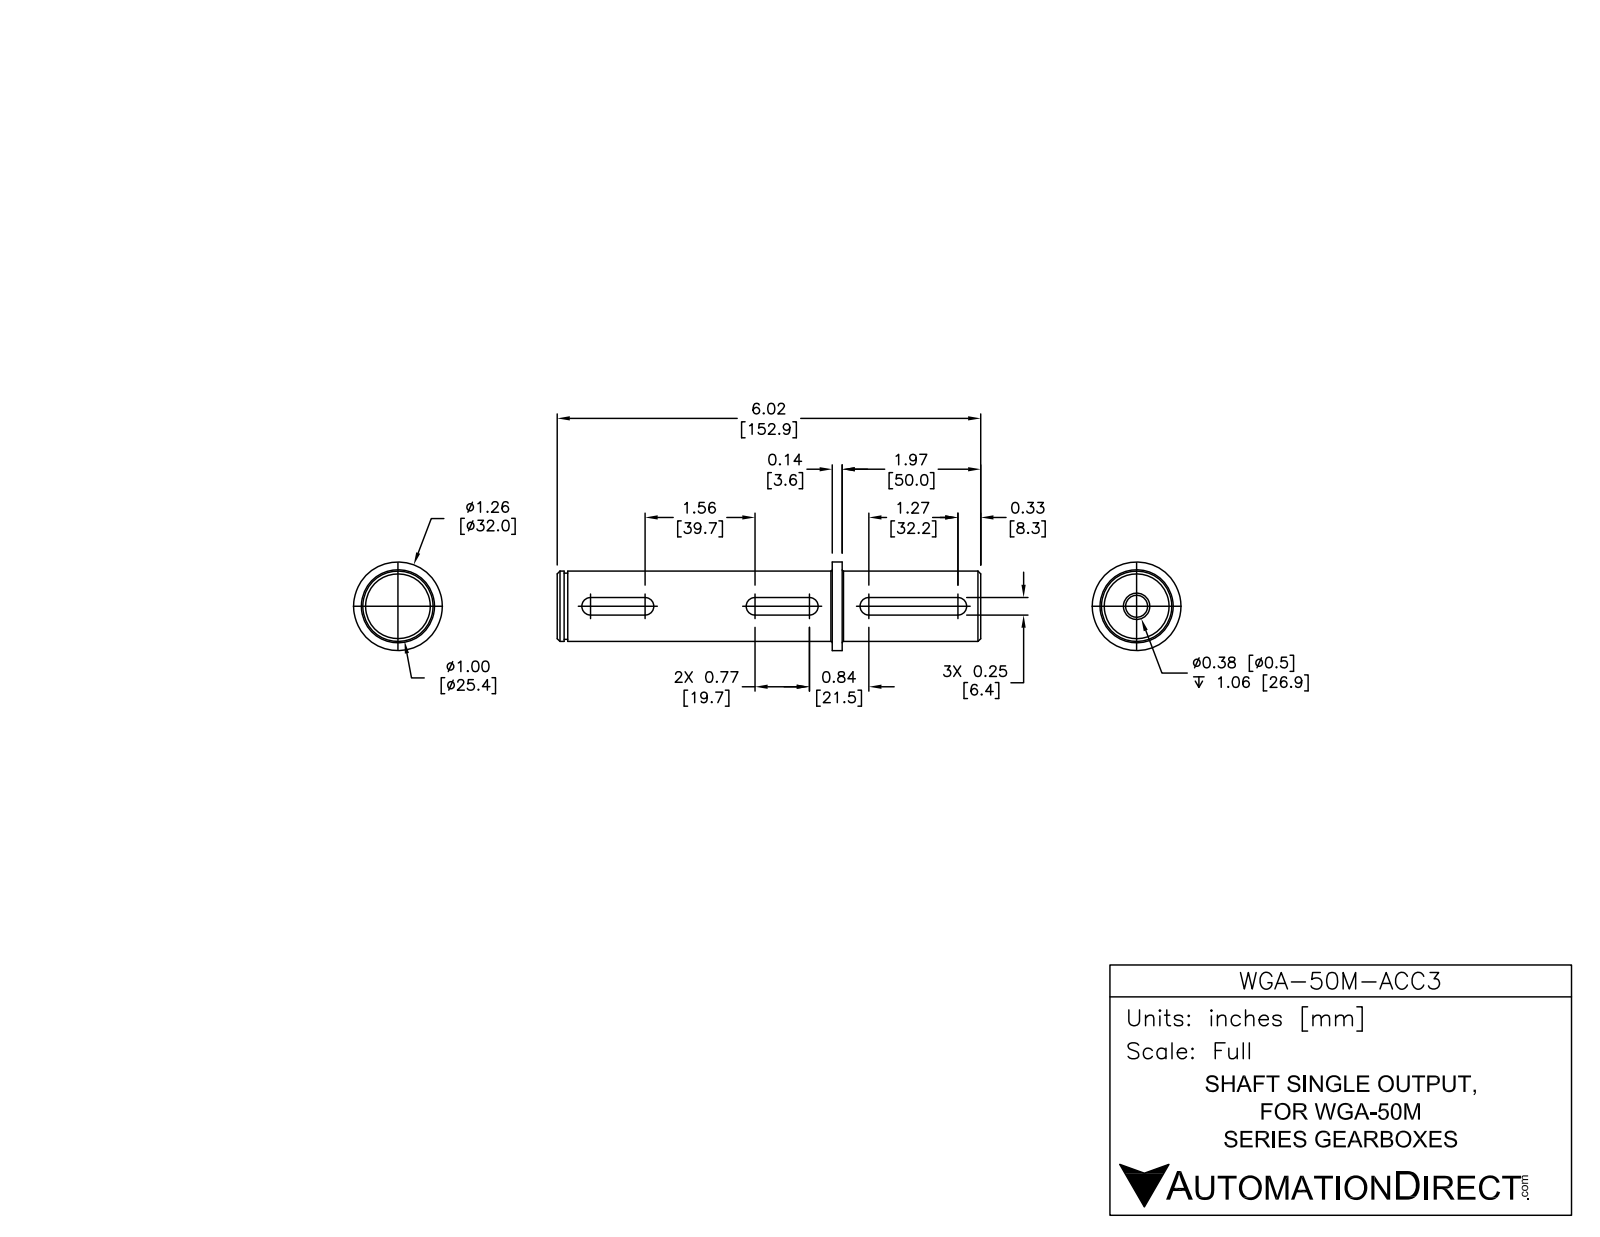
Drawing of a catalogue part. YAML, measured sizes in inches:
part_name: "WGA-50M-ACC3"
step_written_by: "SolidWorks 2014 (AUTOMOTIVE_DESIGN)"
units: inches
bodies: {solids: 1, faces: 46, planar: 16, cylindrical: 20, other: 10}
overall_size: [6.02, 1.26, 1.26]
volume: 4.559
surface_area: 23.7
round_holes:
  - {diameter: 0.313, count: 1}
  - {diameter: 0.375, count: 1}
round_bosses_or_shafts:
  - {diameter: 1.26, count: 1}
  - {diameter: 1, count: 1}
  - {diameter: 0.941, count: 1}
partial_cylinders:
  - {radius: 0.125, count: 6}
face_to_face_distances: [6.02, 4.05, 1.97, 3.909, 0.14, 2.11, 0.25, 0.15, 3.76, 3.9]
